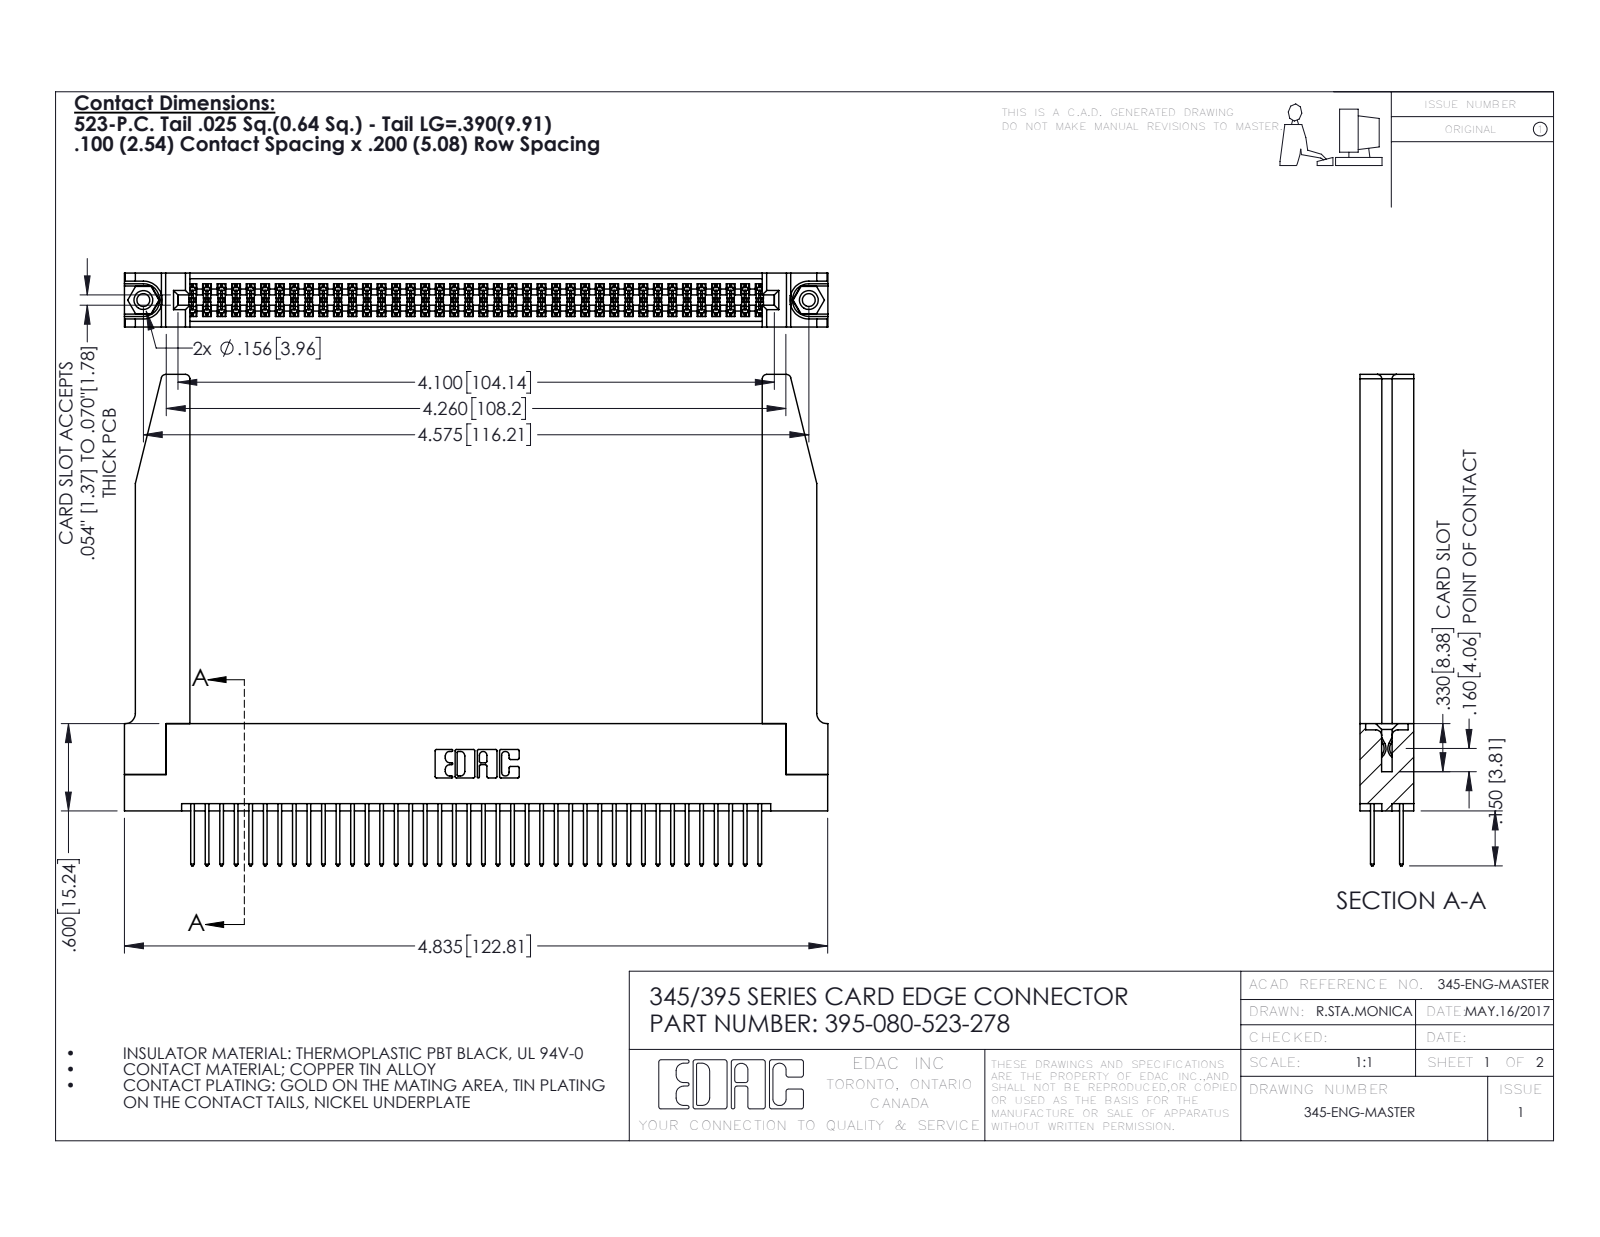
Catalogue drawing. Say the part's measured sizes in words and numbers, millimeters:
The part is named "345-292-001_345-293-123; 345 Part_Flush Mounting Lugs - 0.156 Dia-TH; 395-080-523-278; 345-250-001_345-250-001-102 (+1 more)". Its 3-D file was written by "SolidWorks 2016 (CONFIG_CONTROL_DESIGN)". It is 85 solids with 4360 faces: 2862 planar, 1446 cylindrical and 52 other. Overall it measures 122.8 by 85.8 by 9.4 millimeters. Its volume is 19 840 cubic millimeters and its surface area 25 390 square millimeters. Round holes: 2 of diameter 2.3, 2 of diameter 3.2, 2 of diameter 4, 1 of diameter 1.6. Round bosses or shafts: 2 of diameter 3.9. Partial cylindrical surfaces (rounded edges, fillets, slot ends): 120 of radius 0.2, 80 of radius 0.3, 22 of radius 0.3, 8 of radius 0.8, 6 of radius 0.2, 6 of radius 0.8, 3 of radius 0.7, 2 of radius 0.4. The main face-to-face distances are 1.8, 7.6, 9.4, 5.1, 2.5, 6.9, 0.6, 5.7, 4.4, 3.8. The hole center spacings are 6.9, 110.2, 116.2.
